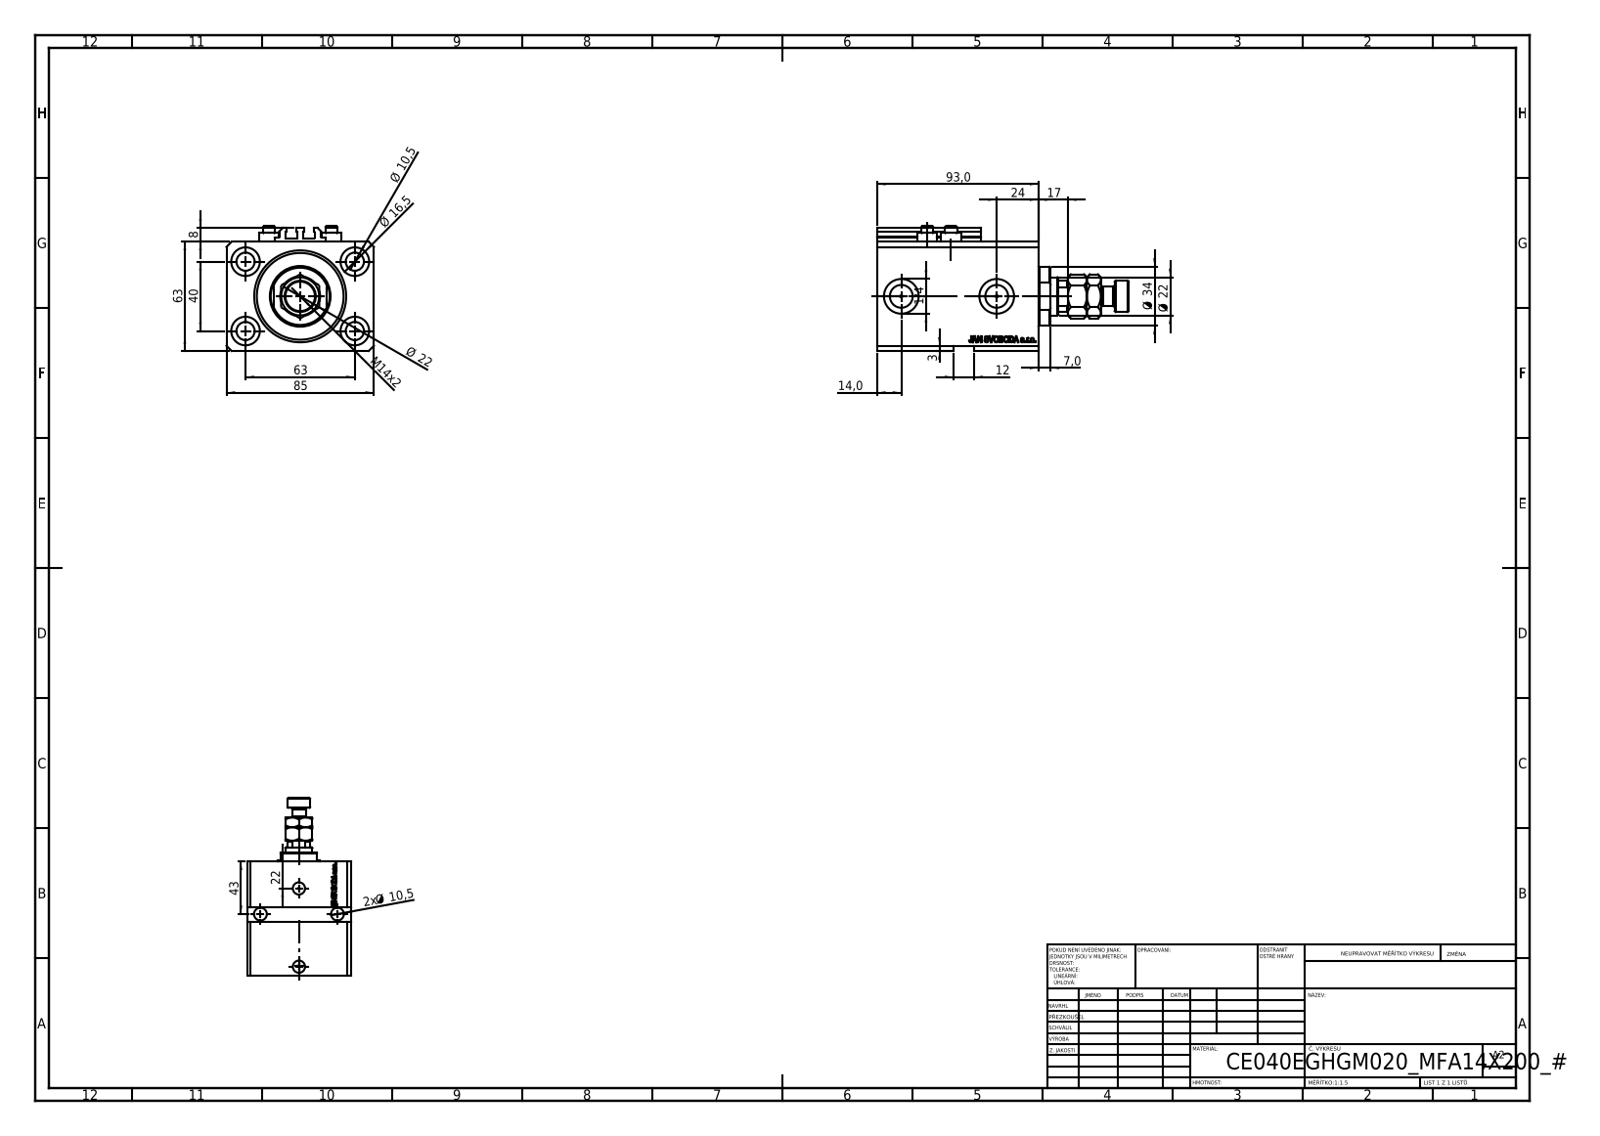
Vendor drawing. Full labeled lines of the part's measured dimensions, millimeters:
Part name (STEP PRODUCT): ALLEN BOLT V250CE; V250CE_E_Body; MFA; V250CE_VC_E (+1 more)
STEP written by: SolidWorks 2019 (CONFIG_CONTROL_DESIGN)
Units: millimetres
Bodies: 9 solids, 1139 faces (551 planar, 130 cylindrical, 458 other)
Overall size (bounding box): 145 × 85 × 72
Volume: 447 941 mm³ · Surface area: 99 017 mm²
Round holes (diameter × count): ⌀10.5 ×6, ⌀1.25 ×4, ⌀4 ×4, ⌀16.5 ×4, ⌀10 ×2, ⌀13.16 ×2, ⌀20 ×2, ⌀12.5 ×1, ⌀22 ×1, ⌀40 ×1, ⌀53 ×1
Round bosses / shafts (diameter × count): ⌀11.6 ×4, ⌀7 ×4, ⌀34 ×1, ⌀18 ×1, ⌀11 ×1
Partial cylindrical surfaces — rounded edges, fillets, slot ends (radius × count): R0.2 ×10, R10.5 ×1
Main face-to-face distances: 63, 85, 93, 17, 76, 11.4, 64.6, 81.6, 3, 65
Hole centre spacings: 37.31, 63, 13.6, 15.4, 24.96, 28.02, 28.43, 33.62
